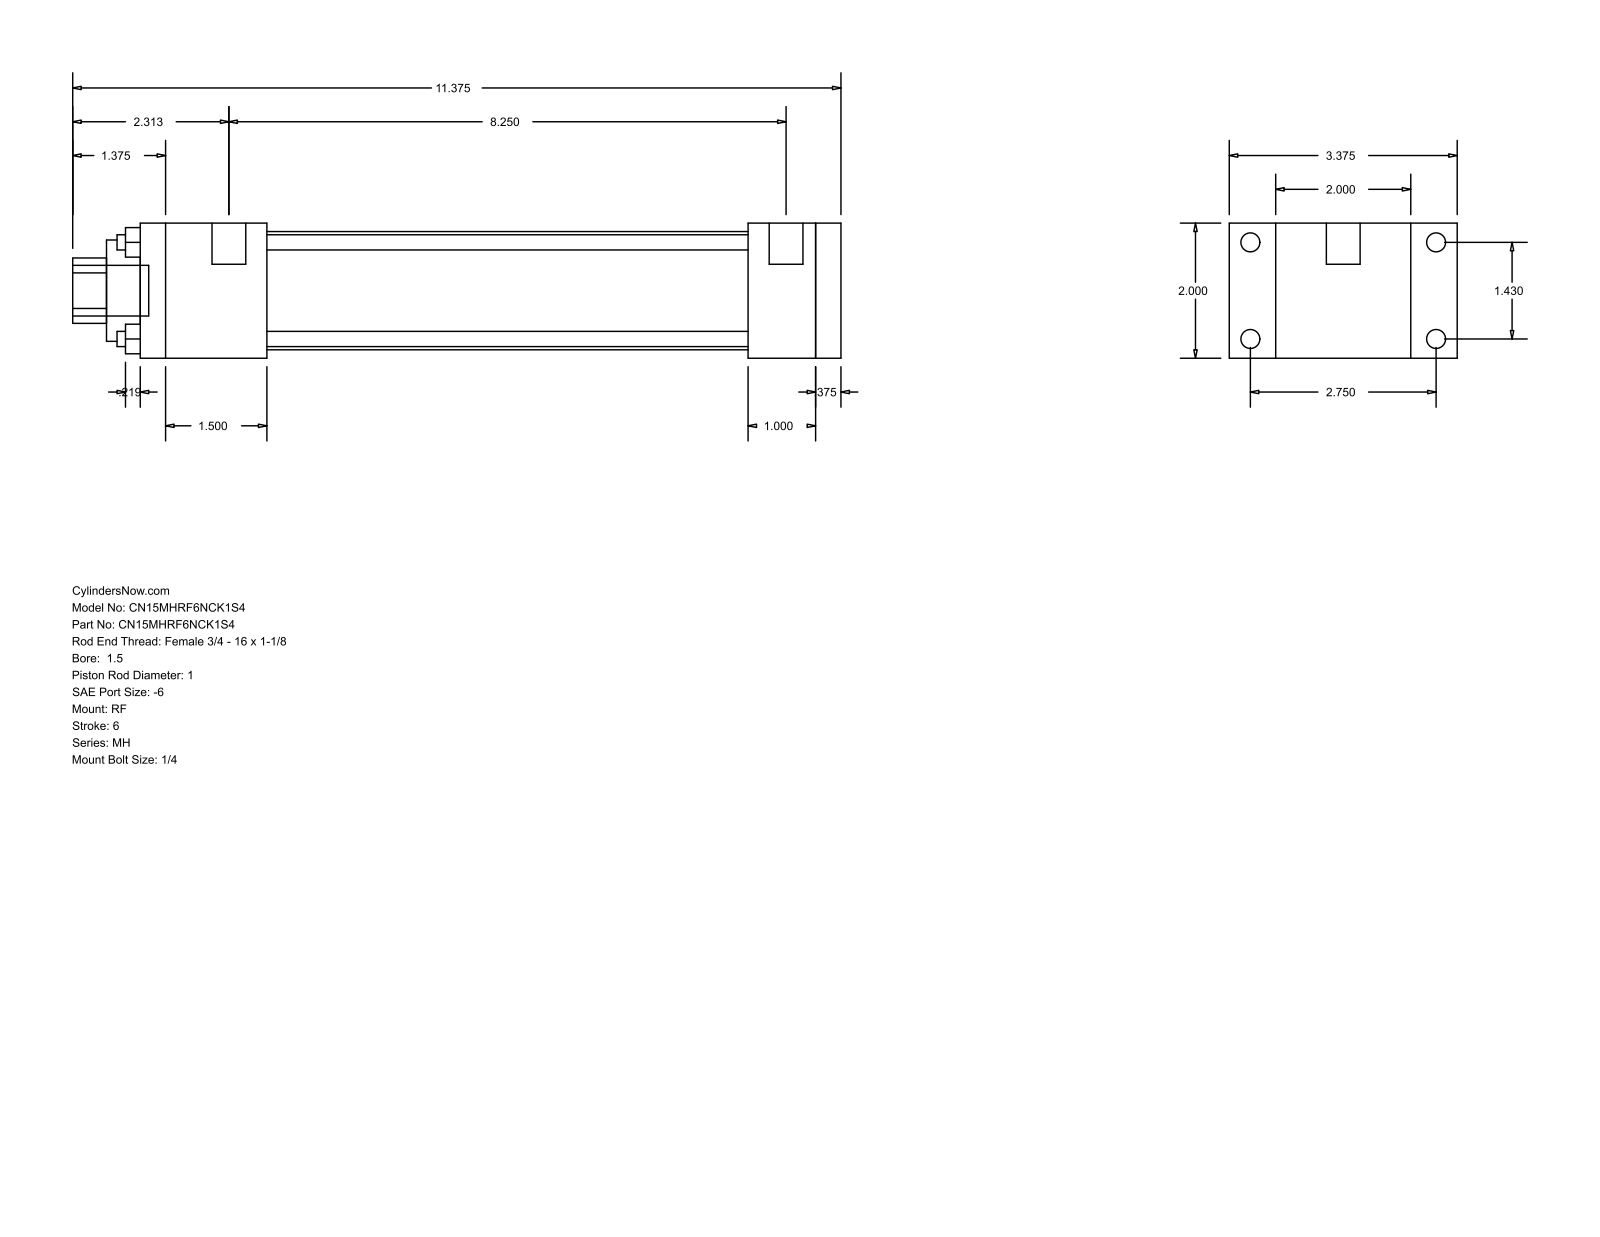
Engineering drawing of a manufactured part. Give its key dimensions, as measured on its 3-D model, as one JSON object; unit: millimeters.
{"part_name": "MH_RF__0150_1", "step_written_by": "GSSL Pune (CONFIG_CONTROL_DESIGN)", "units": "millimeters", "bodies": {"solids": 0, "faces": 92, "planar": 64, "cylindrical": 28, "other": 0}, "overall_size": [288.93, 85.72, 50.8], "round_holes": [[5.71, 4], [25.4, 1], [38.1, 1], [44.45, 1]], "round_bosses_or_shafts": [[7.14, 4], [5.56, 4], [12.7, 2], [19.05, 1]], "partial_cylinders_radius": [[12.29, 1]], "face_to_face_distances": [50.8, 9.53, 254, 25.4, 263.53, 17.46, 68.26, 228.6, 34.93, 47.63], "hole_center_spacings": [25.68, 36.32, 51.36]}
